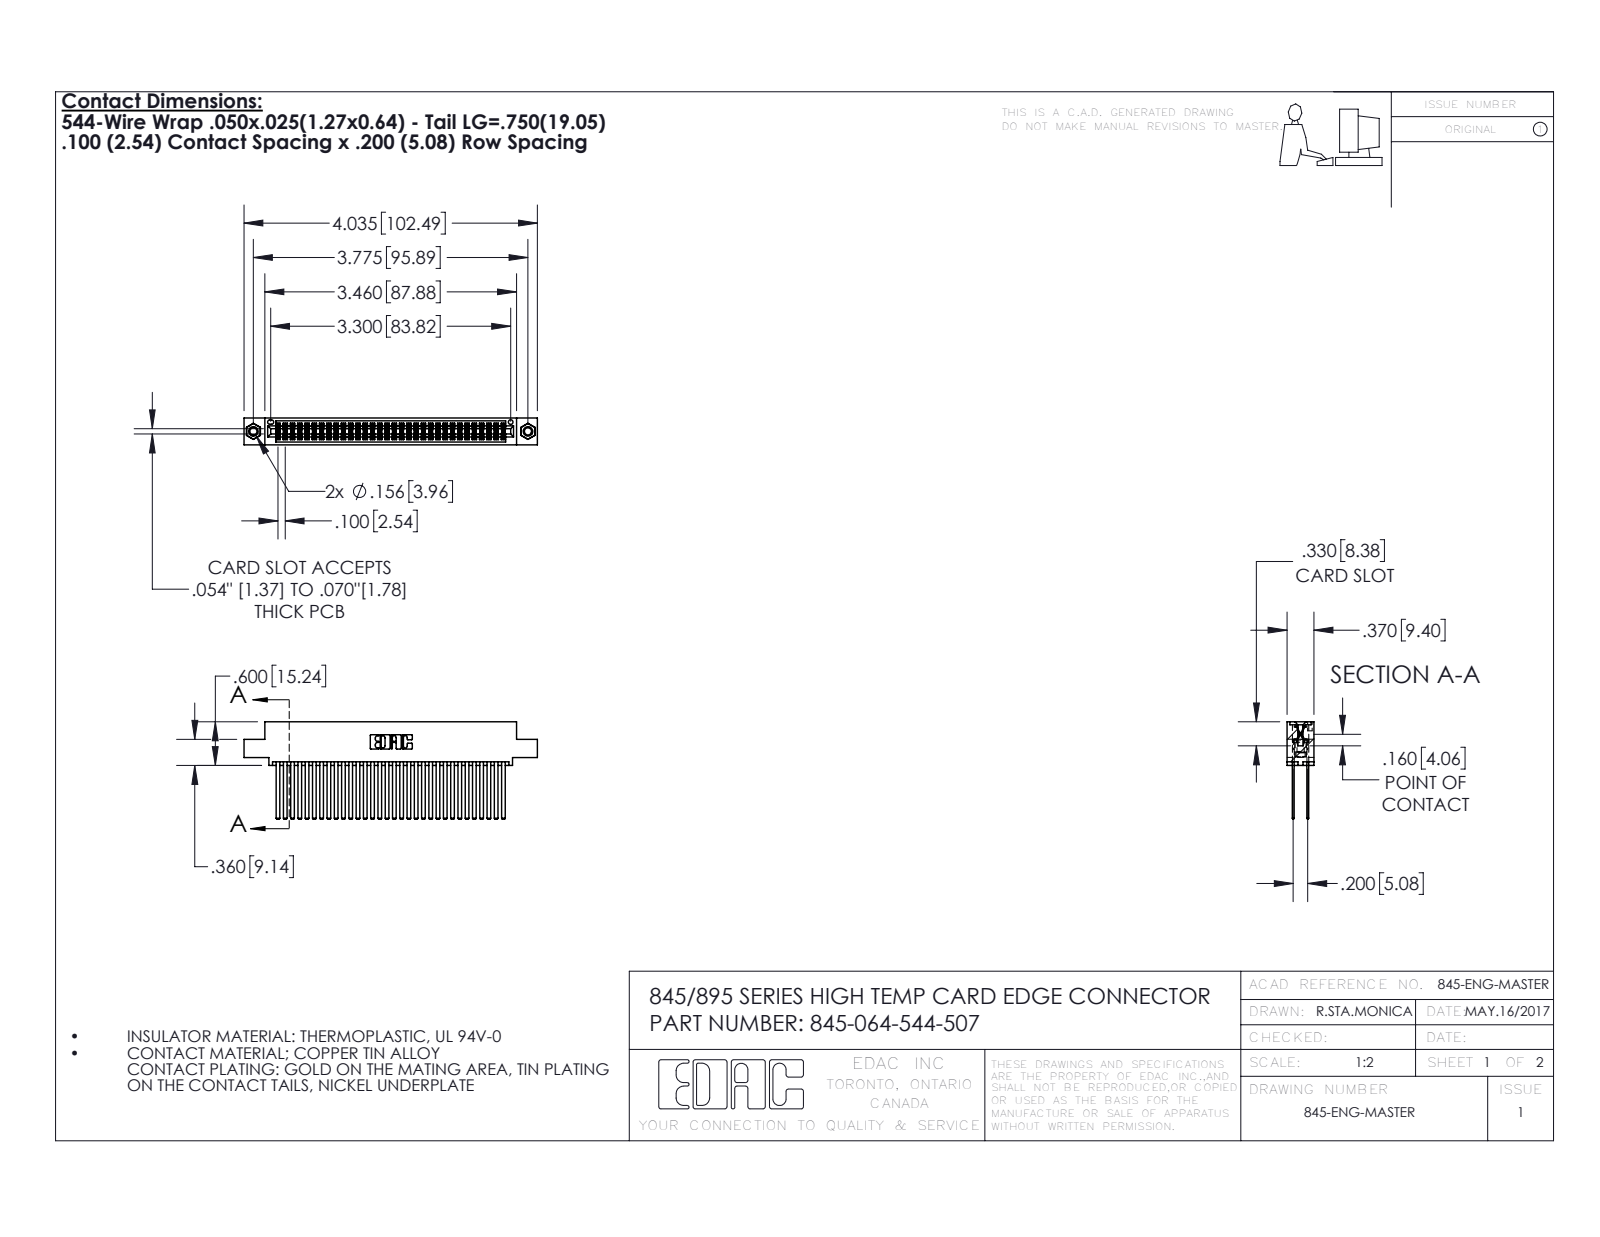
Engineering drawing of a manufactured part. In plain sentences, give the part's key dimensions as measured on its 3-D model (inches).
The part is named "345-064-544-507; 345-292-001_345-293-144; 345-250-001_345-250-005-103; 345 Part_0.110 Offset - 0.156 Dia-TI". Its 3-D file was written by "SolidWorks 2016 (CONFIG_CONTROL_DESIGN)". It is 67 solids with 3006 faces: 1972 planar, 1018 cylindrical and 16 other. Overall it measures 4.035 by 1.337 by 0.37 inches. Its volume is 0.651 cubic inches and its surface area 28.42 square inches. Round holes: 2 of diameter 0.098, 2 of diameter 0.125, 2 of diameter 0.156, 1 of diameter 0.064. Round bosses or shafts: 2 of diameter 0.155. Partial cylindrical surfaces (rounded edges, fillets, slot ends): 96 of radius 0.006, 22 of radius 0.01, 6 of radius 0.007, 6 of radius 0.031, 3 of radius 0.026, 2 of radius 0.014, 2 of radius 0.019, 2 of radius 0.022. The main face-to-face distances are 0.2, 0.025, 0.072, 0.098, 0.272, 0.298, 0.225, 0.175, 0.37, 0.05. The hole center spacings are 0.27, 3.54, 3.775.
